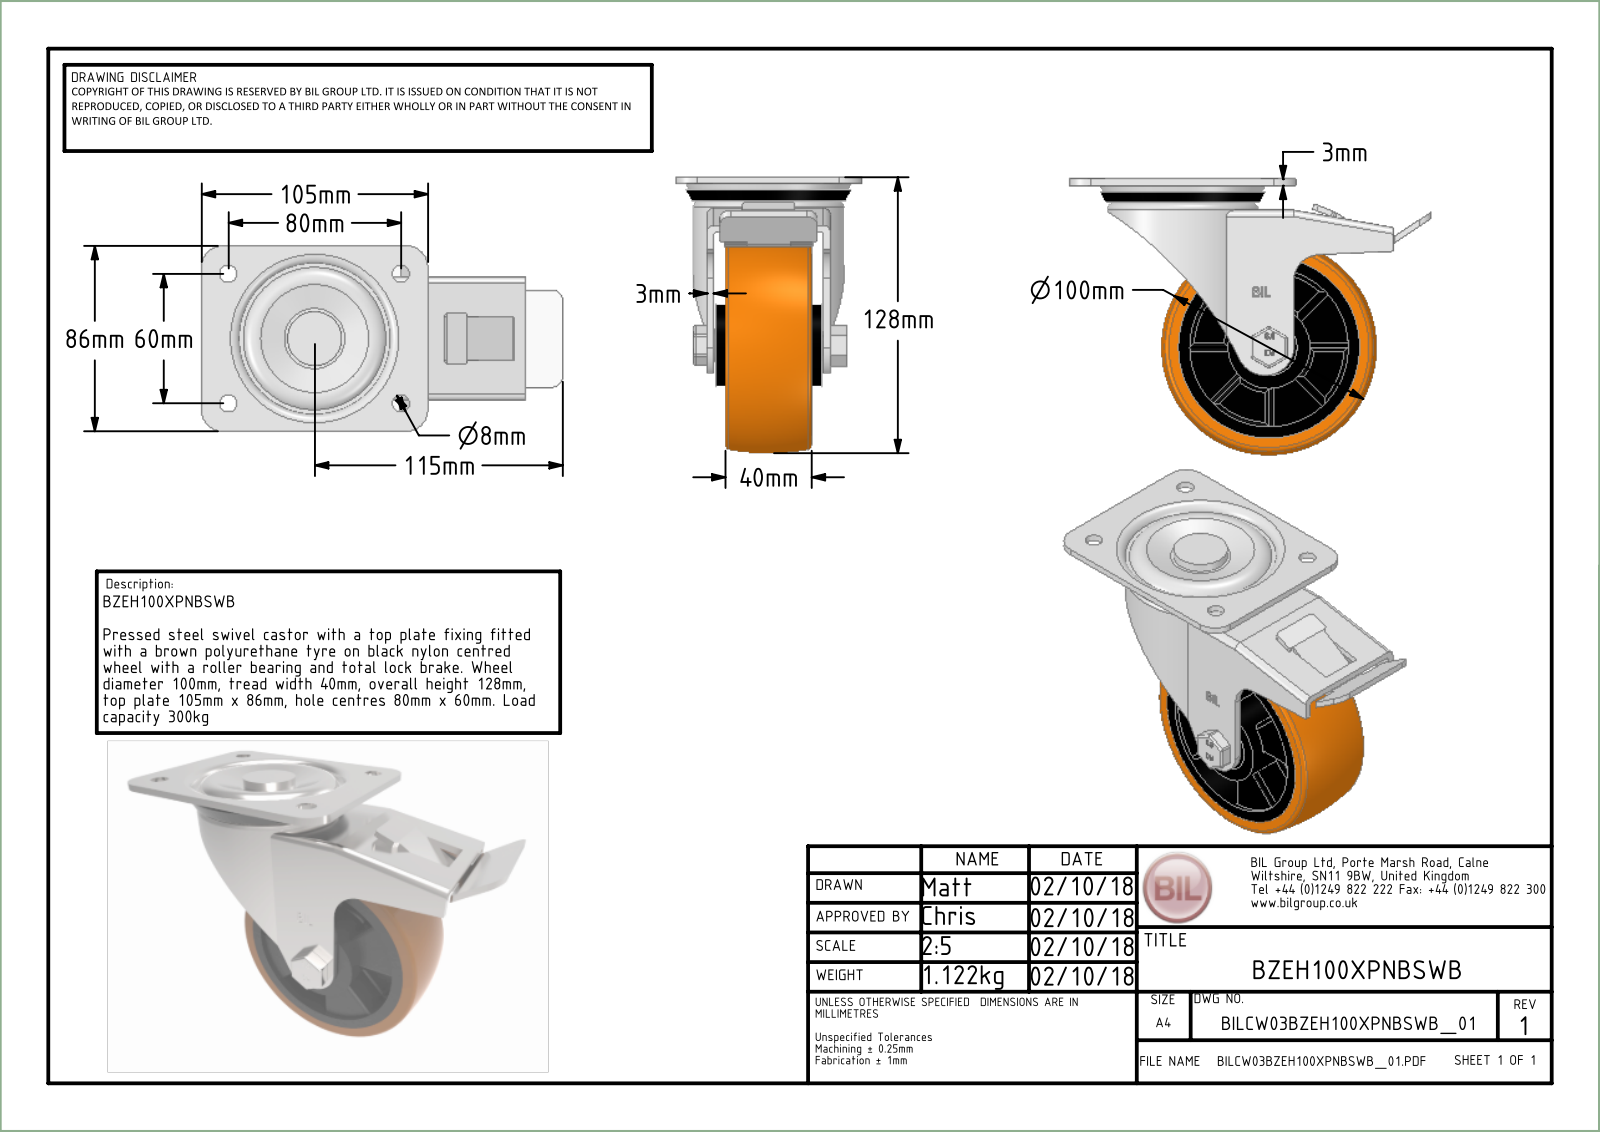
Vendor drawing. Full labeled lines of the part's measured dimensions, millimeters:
Part name (STEP PRODUCT): BZEH100XPNBSWB v3; BZEH100ASSWB v1; ZINC PLATED, PRESSED STEEL TOP PLATE; ZINC PLATED, PRESSED STEEL TOP PLATE Geometry (+7 more)
STEP written by: Autodesk Translation Framework v14.10.0.0 (AUTOMOTIVE_DESIGN)
Units: millimetres
Bodies: 42 solids, 886 faces (394 planar, 182 cylindrical, 310 other)
Overall size (bounding box): 167.5 × 128 × 86
Volume: 335 685 mm³ · Surface area: 164 864 mm²
Round holes (diameter × count): ⌀8 ×1, ⌀10 ×1, ⌀10.2 ×1, ⌀10.3 ×1, ⌀12 ×1, ⌀15 ×1, ⌀15.5 ×1, ⌀26 ×1, ⌀27 ×1, ⌀30 ×1, ⌀64 ×1, ⌀73 ×1
Round bosses / shafts (diameter × count): ⌀4 ×8, ⌀70 ×1, ⌀54 ×1, ⌀37 ×1, ⌀26.9 ×1, ⌀25 ×1, ⌀22.5 ×1, ⌀21 ×1
Partial cylindrical surfaces — rounded edges, fillets, slot ends (radius × count): R0.5 ×20, R4.5 ×9, R1 ×8, R0.75 ×6, R1.5 ×6, R3 ×4, R10 ×4, R2 ×3
Main face-to-face distances: 3, 5, 1, 2, 10, 4, 5.5, 7, 54, 8.5
